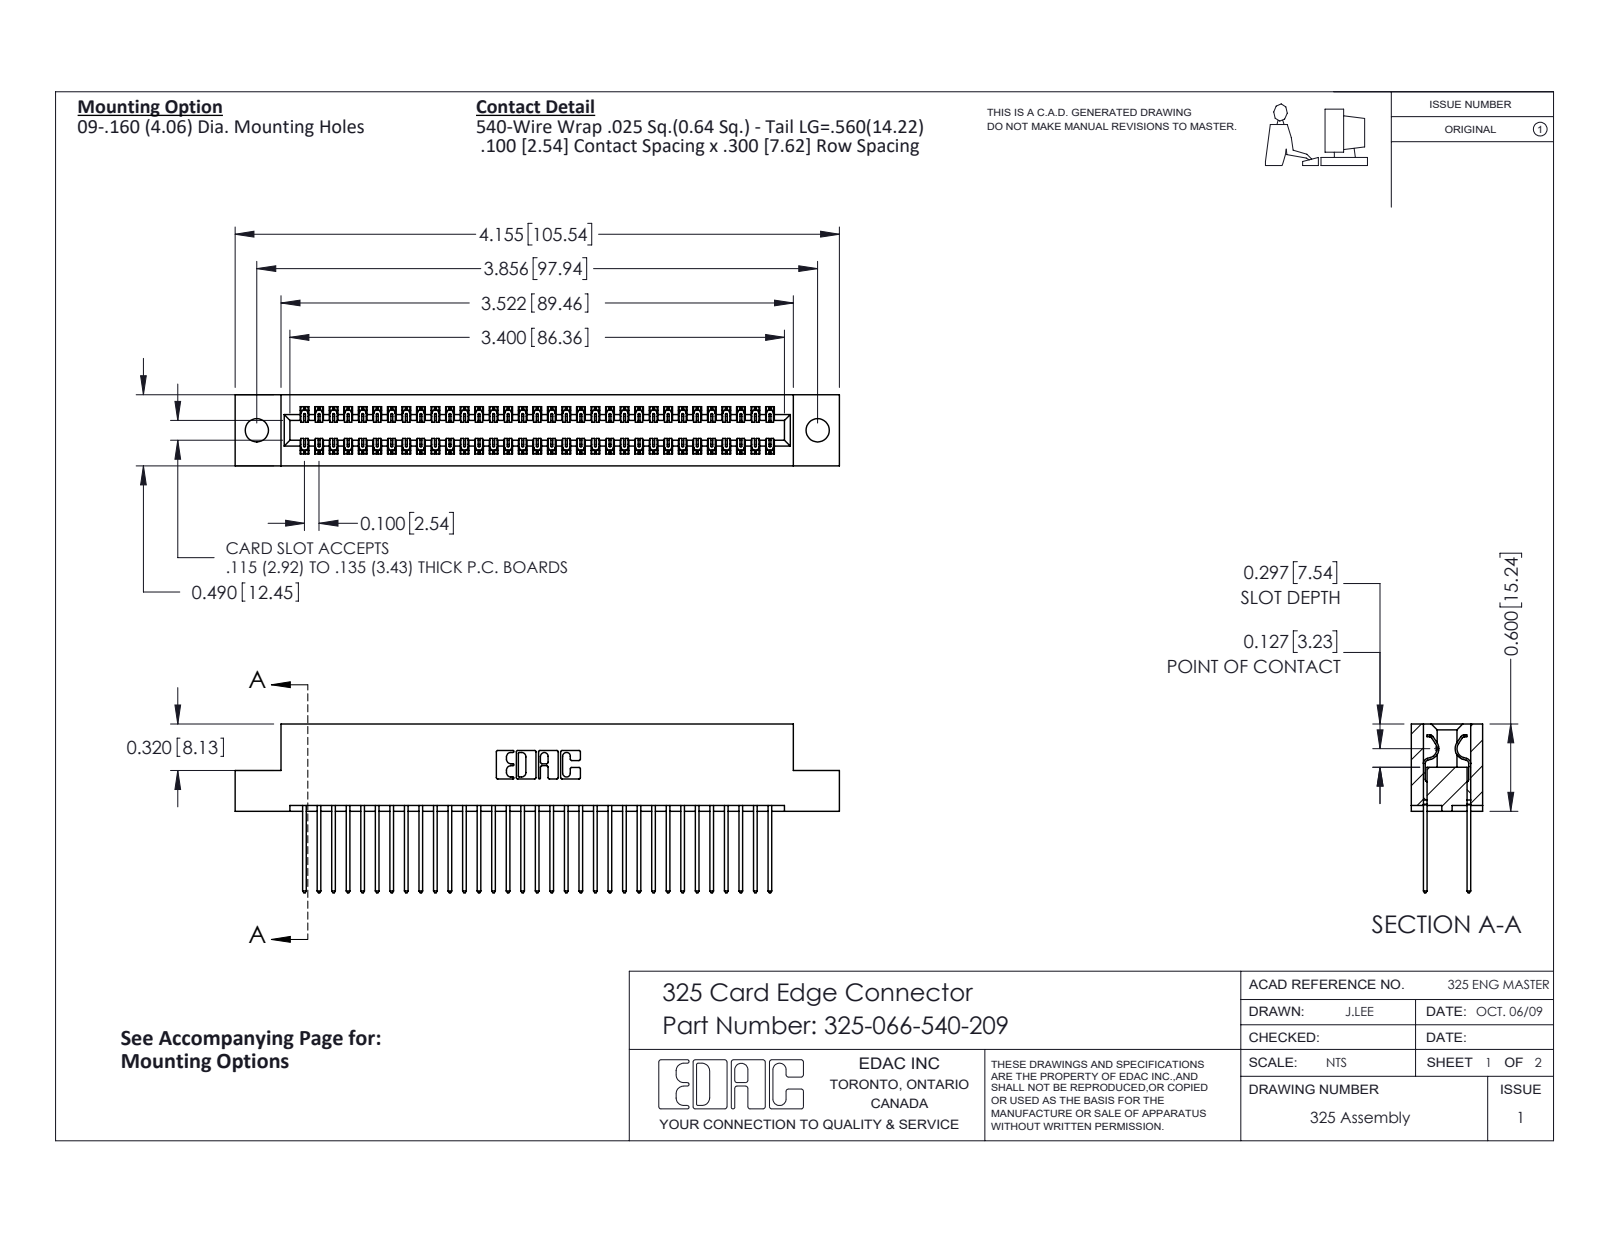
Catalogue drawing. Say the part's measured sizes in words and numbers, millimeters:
The part is named "325-292-001_325-293-140; 325-066-540-209; 325 Part_.160 TH". Its 3-D file was written by "SolidWorks 2016 (CONFIG_CONTROL_DESIGN)". It is 67 solids with 3546 faces: 2446 planar, 1100 cylindrical and 0 other. Overall it measures 105.5 by 29.5 by 12.4 millimeters. Its volume is 13 600 cubic millimeters and its surface area 17 320 square millimeters. Round holes: 2 of diameter 4.1. Partial cylindrical surfaces (rounded edges, fillets, slot ends): 99 of radius 0.2, 66 of radius 0.3, 22 of radius 0.3, 6 of radius 0.2, 6 of radius 0.8, 3 of radius 0.7, 2 of radius 0.4, 2 of radius 0.6. The main face-to-face distances are 2.1, 10.3, 7.6, 2.7, 9.7, 0.6, 12.4, 8.3, 7, 14.2. The hole center spacings are 97.9.
